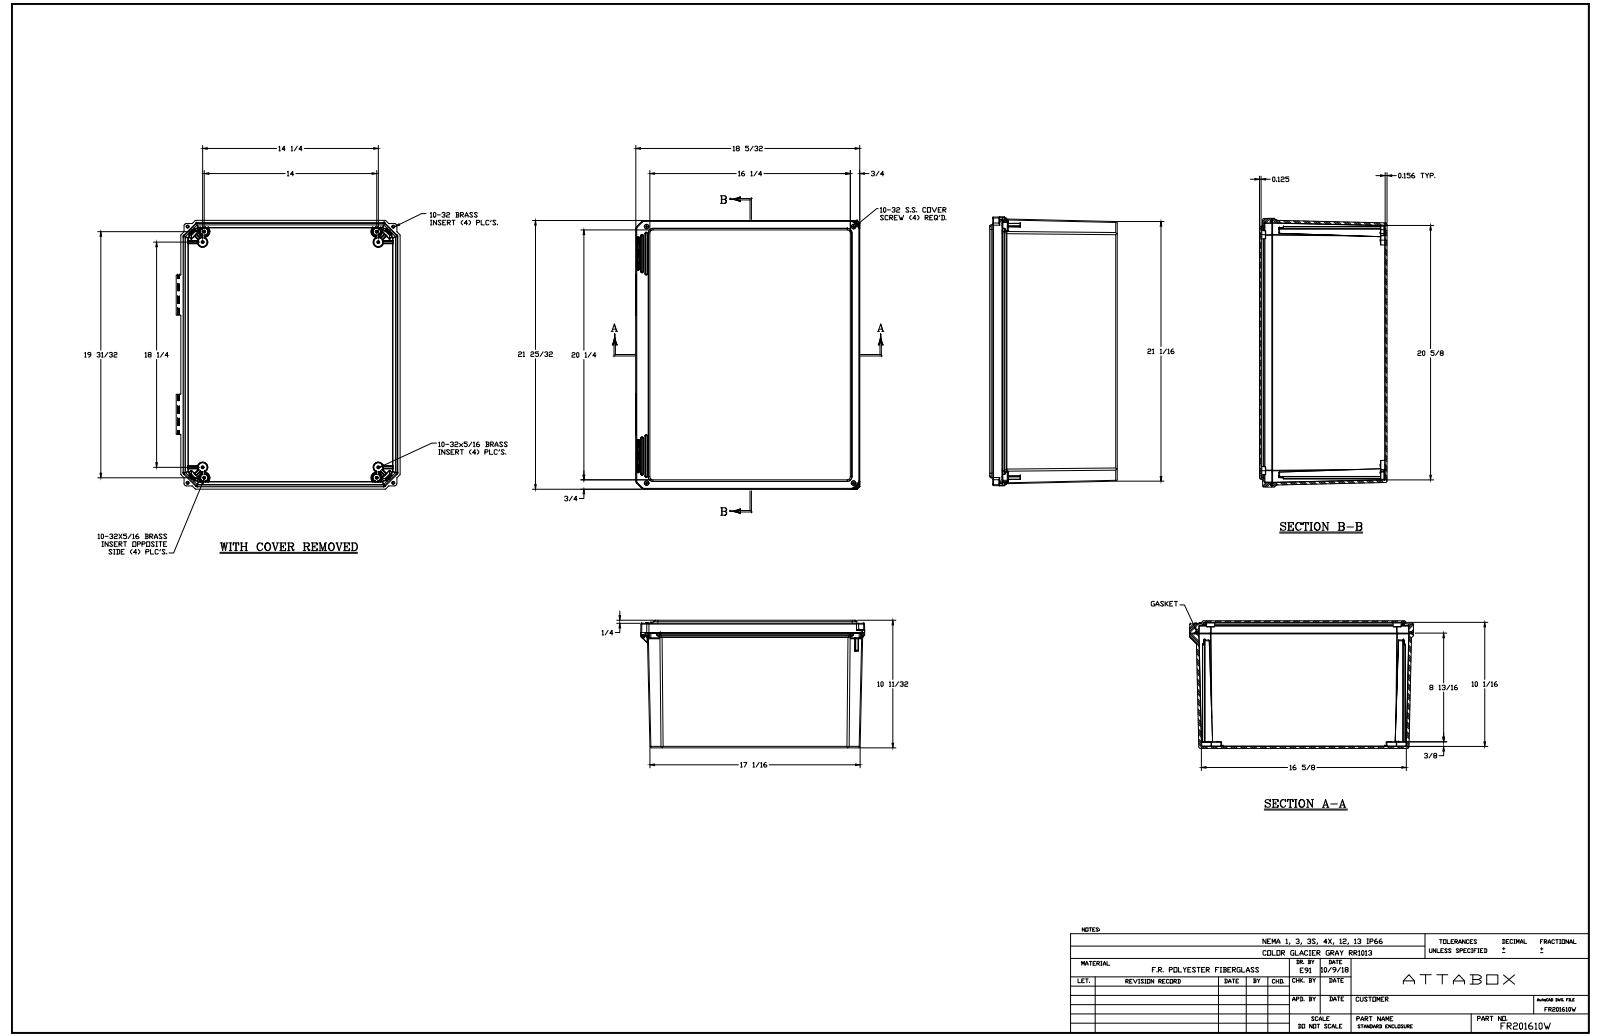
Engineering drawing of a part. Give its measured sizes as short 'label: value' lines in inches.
name: FR201610W
written by: SolidWorks 2018 (AUTOMOTIVE_DESIGN)
unit: in
bodies: 27 solids, 2145 faces (738 planar, 781 cylindrical, 626 other)
size: 21.791 × 18.166 × 10.344
volume: 283 in³; area: 3 173 in²
holes: 16× ⌀0.156, 8× ⌀0.152, 4× ⌀0.252, 4× ⌀0.253, 2× ⌀0.137, 2× ⌀0.219, 2× ⌀0.227, 2× ⌀0.313
bosses: 16× ⌀0.246, 4× ⌀0.45, 4× ⌀0.199, 1× ⌀0.435, 1× ⌀0.435
rounds: 177× R0.01, 88× R0.005, 49× R0.02, 41× R0.03, 24× R0.03, 24× R0.09, 24× R0.096, 22× R0.063
face distances: 0.125, 0.156, 10.187, 10.343, 10.219, 10.063, 0.212, 0.21, 0.25, 0.125
hole spacings: 15.572, 0.862, 14.151, 15.4, 19.104, 19.561, 16.79, 1.456
